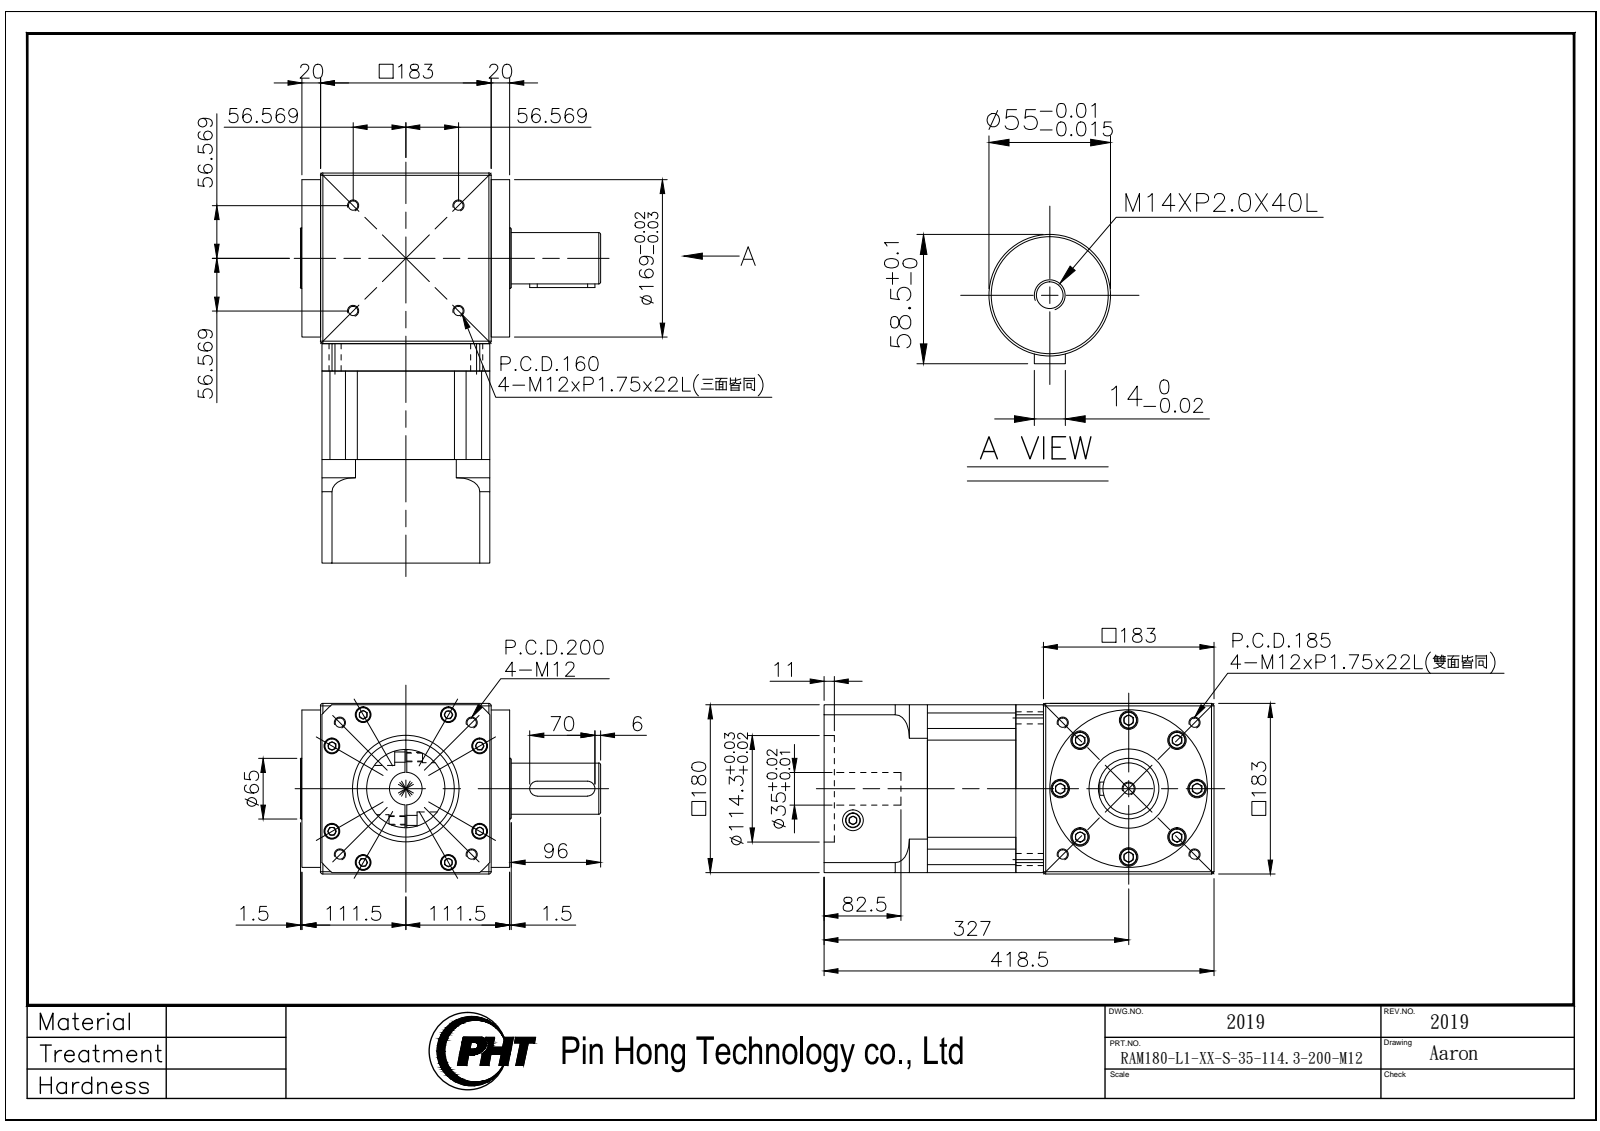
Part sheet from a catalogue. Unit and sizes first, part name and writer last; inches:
Units: inches
Overall size (bounding box): 16.476 × 12.677 × 7.205
Round holes (diameter × count): ⌀0.402 ×20, ⌀0.433 ×8, ⌀0.551 ×8, ⌀0.669 ×8, ⌀0.787 ×8, ⌀0.512 ×4, ⌀0.886 ×2, ⌀0.157 ×1, ⌀0.472 ×1, ⌀1.378 ×1, ⌀4.094 ×1, ⌀4.5 ×1
Round bosses / shafts (diameter × count): ⌀0.72 ×8, ⌀0.63 ×8, ⌀0.709 ×4, ⌀6.654 ×1, ⌀6.299 ×1, ⌀3.346 ×1, ⌀3.307 ×1, ⌀2.559 ×1
Partial cylindrical surfaces — rounded edges, fillets, slot ends (radius × count): R0.492 ×4, R0.276 ×2, R4.094 ×1, R4.134 ×1, R4.724 ×1
Main face-to-face distances: 0.059, 7.146, 7.205, 7.087, 3.74, 4.902, 1.161, 8.366, 0.846, 12.106
Hole centre spacings: 3.602, 0.989, 1.039, 1.198, 2.215, 2.595, 2.894, 4.092
Volume: 854.3 in³ · Surface area: 1 211 in²
Bodies: 4 solids, 807 faces (348 planar, 281 cylindrical, 178 other)
Part name (STEP PRODUCT): RAM180-L1-XX-S-35-114.3-200-M12_2019
STEP written by: SolidWorks 2016 (AUTOMOTIVE_DESIGN)
